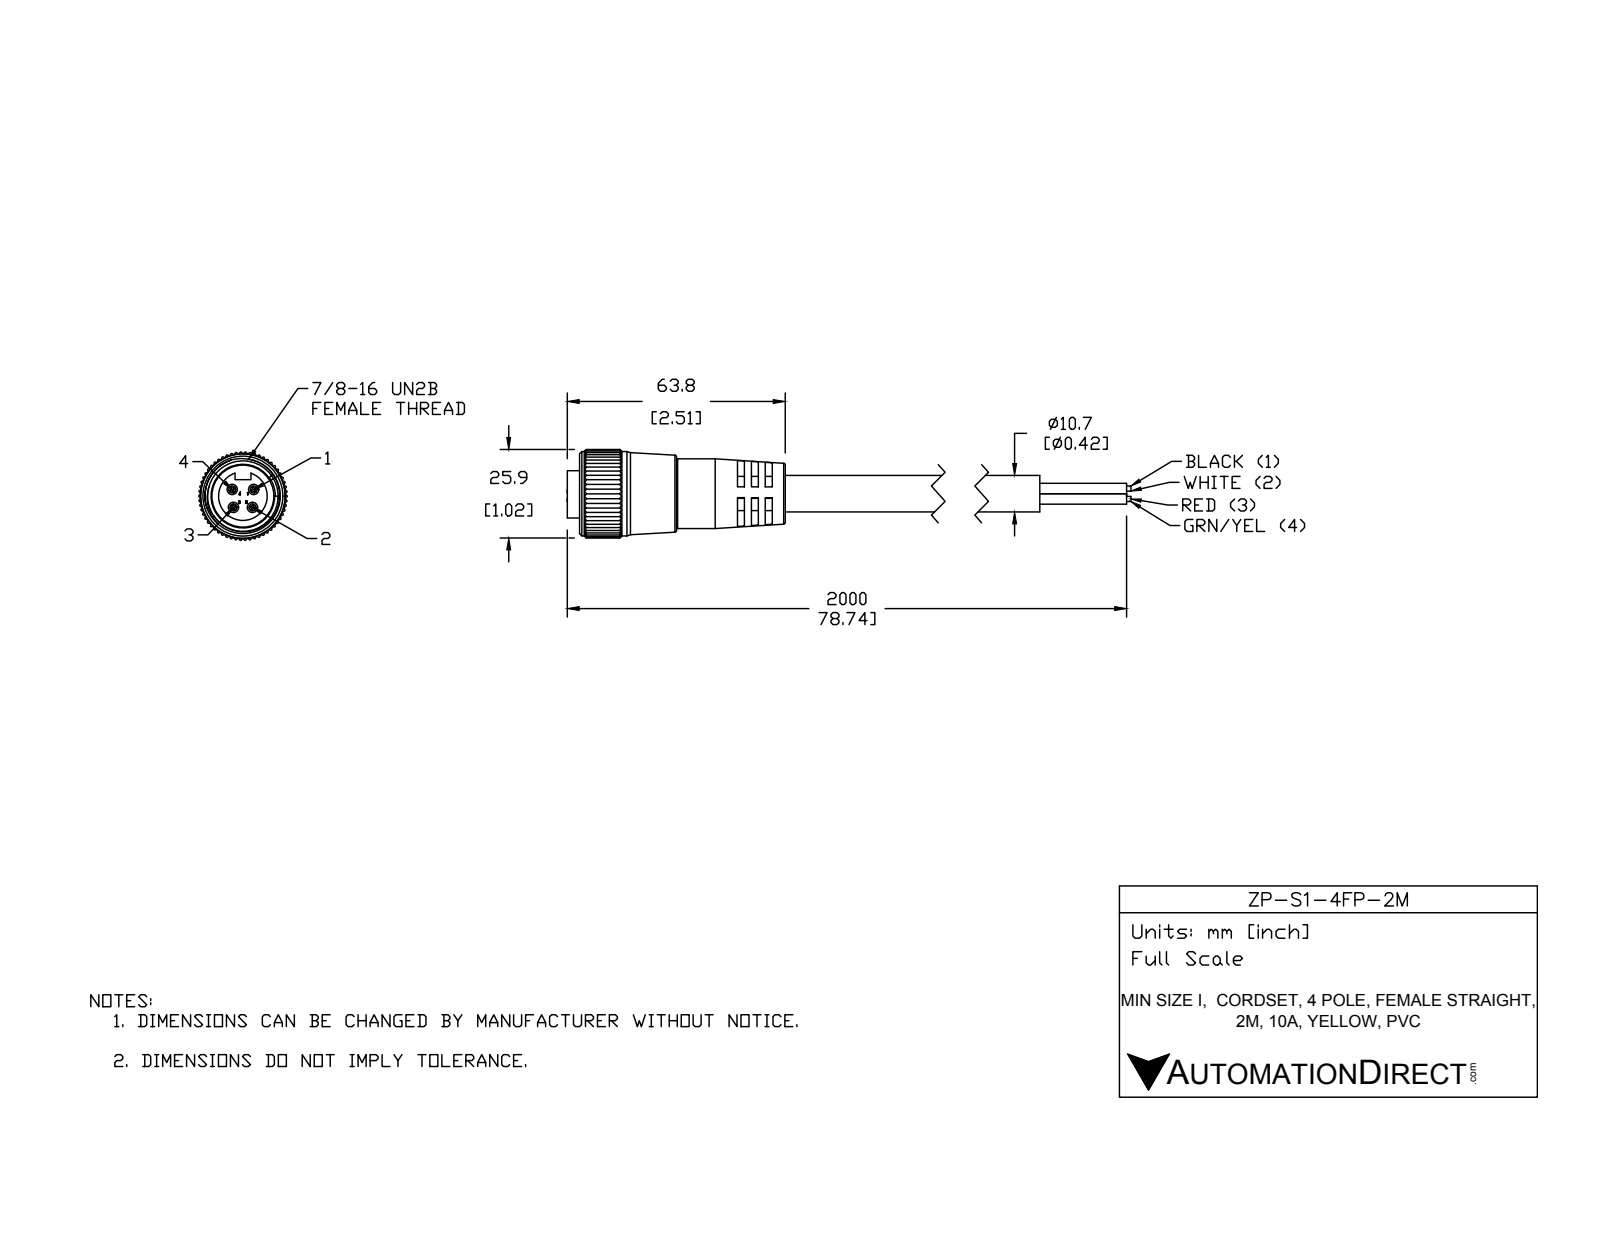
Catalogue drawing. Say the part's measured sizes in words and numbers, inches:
The part is named "ZP-S1-4FP-2M". Its 3-D file was written by "SolidWorks 2015 (AUTOMOTIVE_DESIGN)". It is 2 solids with 558 faces: 208 planar, 308 cylindrical and 42 other. Overall it measures 4.295 by 2.083 by 1.017 inches. Its volume is 1.685 cubic inches and its surface area 18.62 square inches. Round holes: 4 of diameter 0.12, 1 of diameter 0.714, 1 of diameter 0.81, 1 of diameter 0.827. Round bosses or shafts: 2 of diameter 0.42, 1 of diameter 0.972, 1 of diameter 0.803, 1 of diameter 0.768, 1 of diameter 0.56. Partial cylindrical surfaces (rounded edges, fillets, slot ends): 165 of radius 0.01, 1 of radius 0.207, 1 of radius 0.509. The main face-to-face distances are 0.159, 0.079, 0.08, 0.237, 0.317, 0.546, 0.467, 0.387, 0.309, 0.239. The hole center spacings are 0.144, 0.206, 0.17, 0.17, 0.22, 0.246, 0.311, 0.311.
